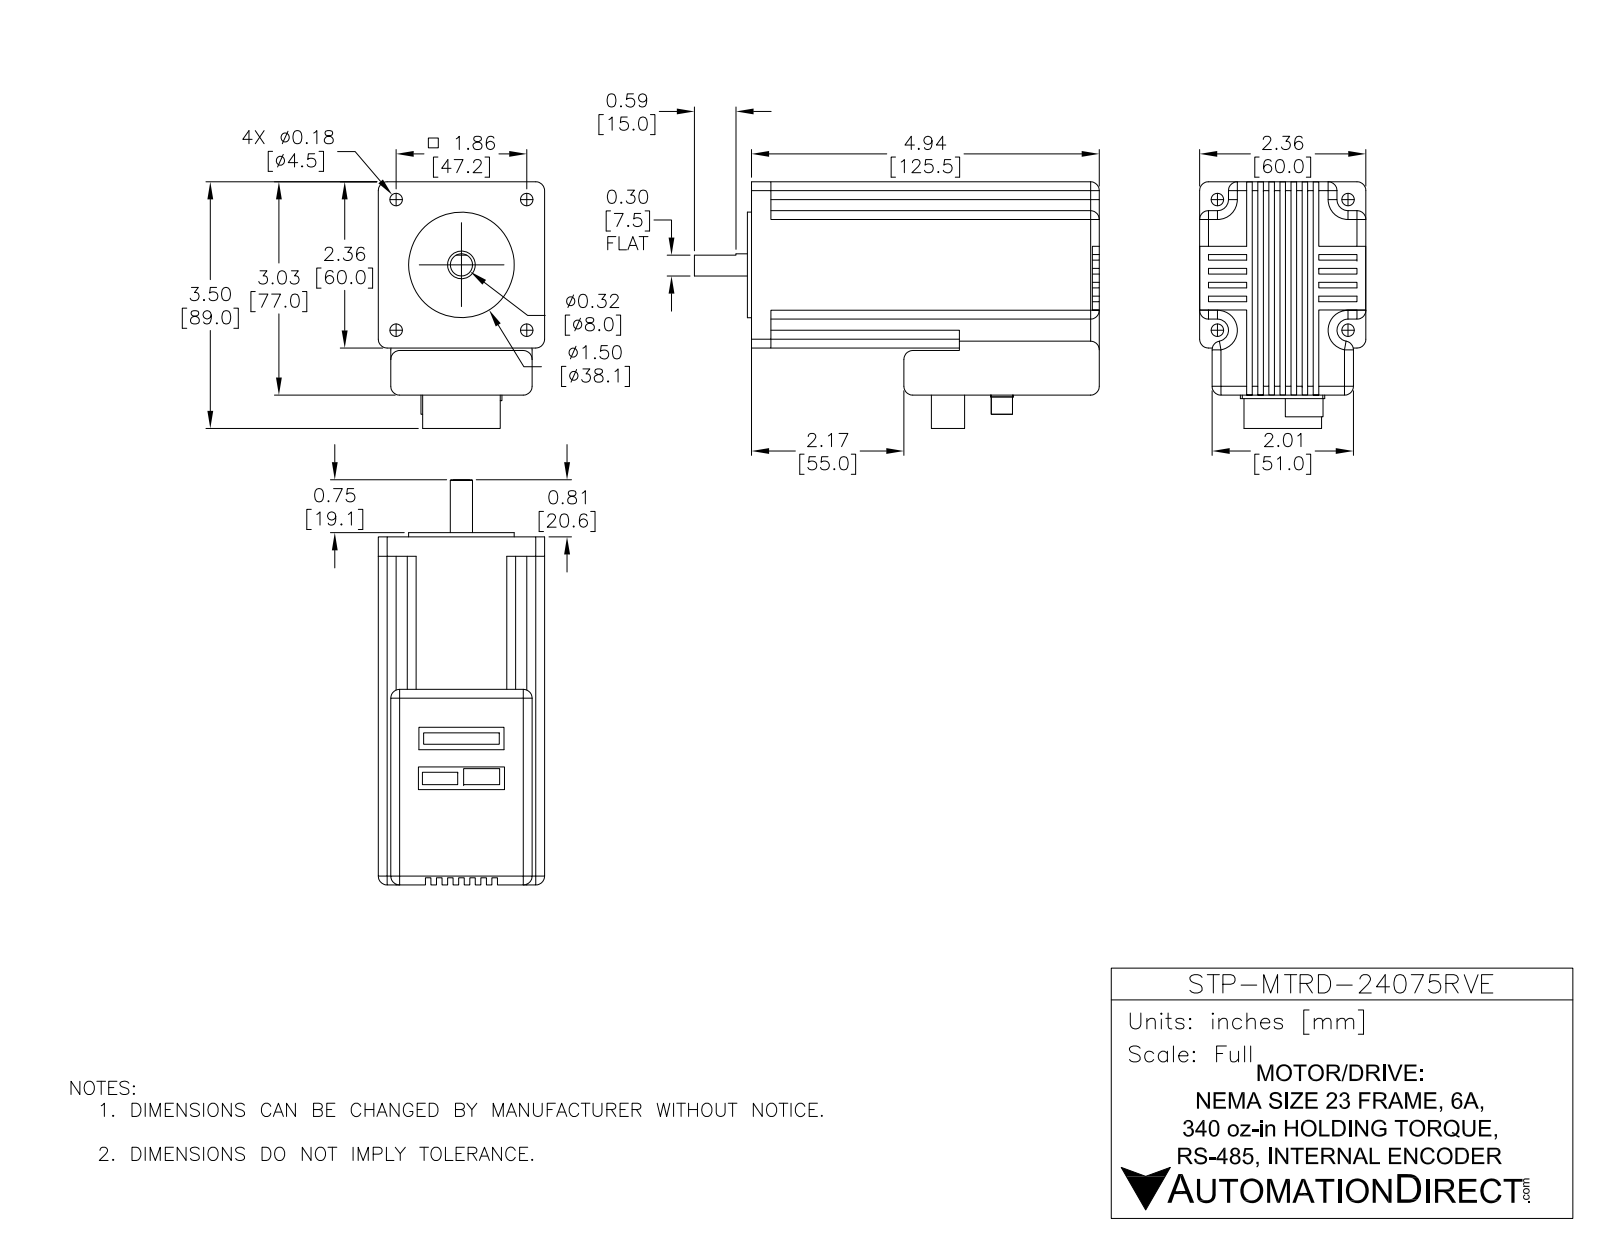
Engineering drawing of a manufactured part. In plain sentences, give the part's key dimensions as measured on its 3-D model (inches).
The part is named "STP-MTRD-24075RVE". Its 3-D file was written by "SolidWorks 2017 (AUTOMOTIVE_DESIGN)". It is 1 solid with 693 faces: 261 planar, 292 cylindrical and 140 other. Overall it measures 5.756 by 3.081 by 2.362 inches. Its volume is 27.3 cubic inches and its surface area 78.09 square inches. Round holes: 4 of diameter 0.177, 1 of diameter 0.394, 1 of diameter 0.748. Round bosses or shafts: 4 of diameter 0.217, 2 of diameter 0.22, 1 of diameter 1.5, 1 of diameter 0.315. Partial cylindrical surfaces (rounded edges, fillets, slot ends): 122 of radius 0.02, 28 of radius 0.126, 7 of radius 0.026, 6 of radius 0.098, 4 of radius 0.157, 4 of radius 0.431, 3 of radius 0.026, 3 of radius 0.027. The main face-to-face distances are 2.362, 0.079, 0.157, 0.236, 0.394, 0.315, 0.472, 0.669, 0.411, 1.952. The hole center spacings are 1.312, 1.856, 1.307, 1.318, 2.625.
